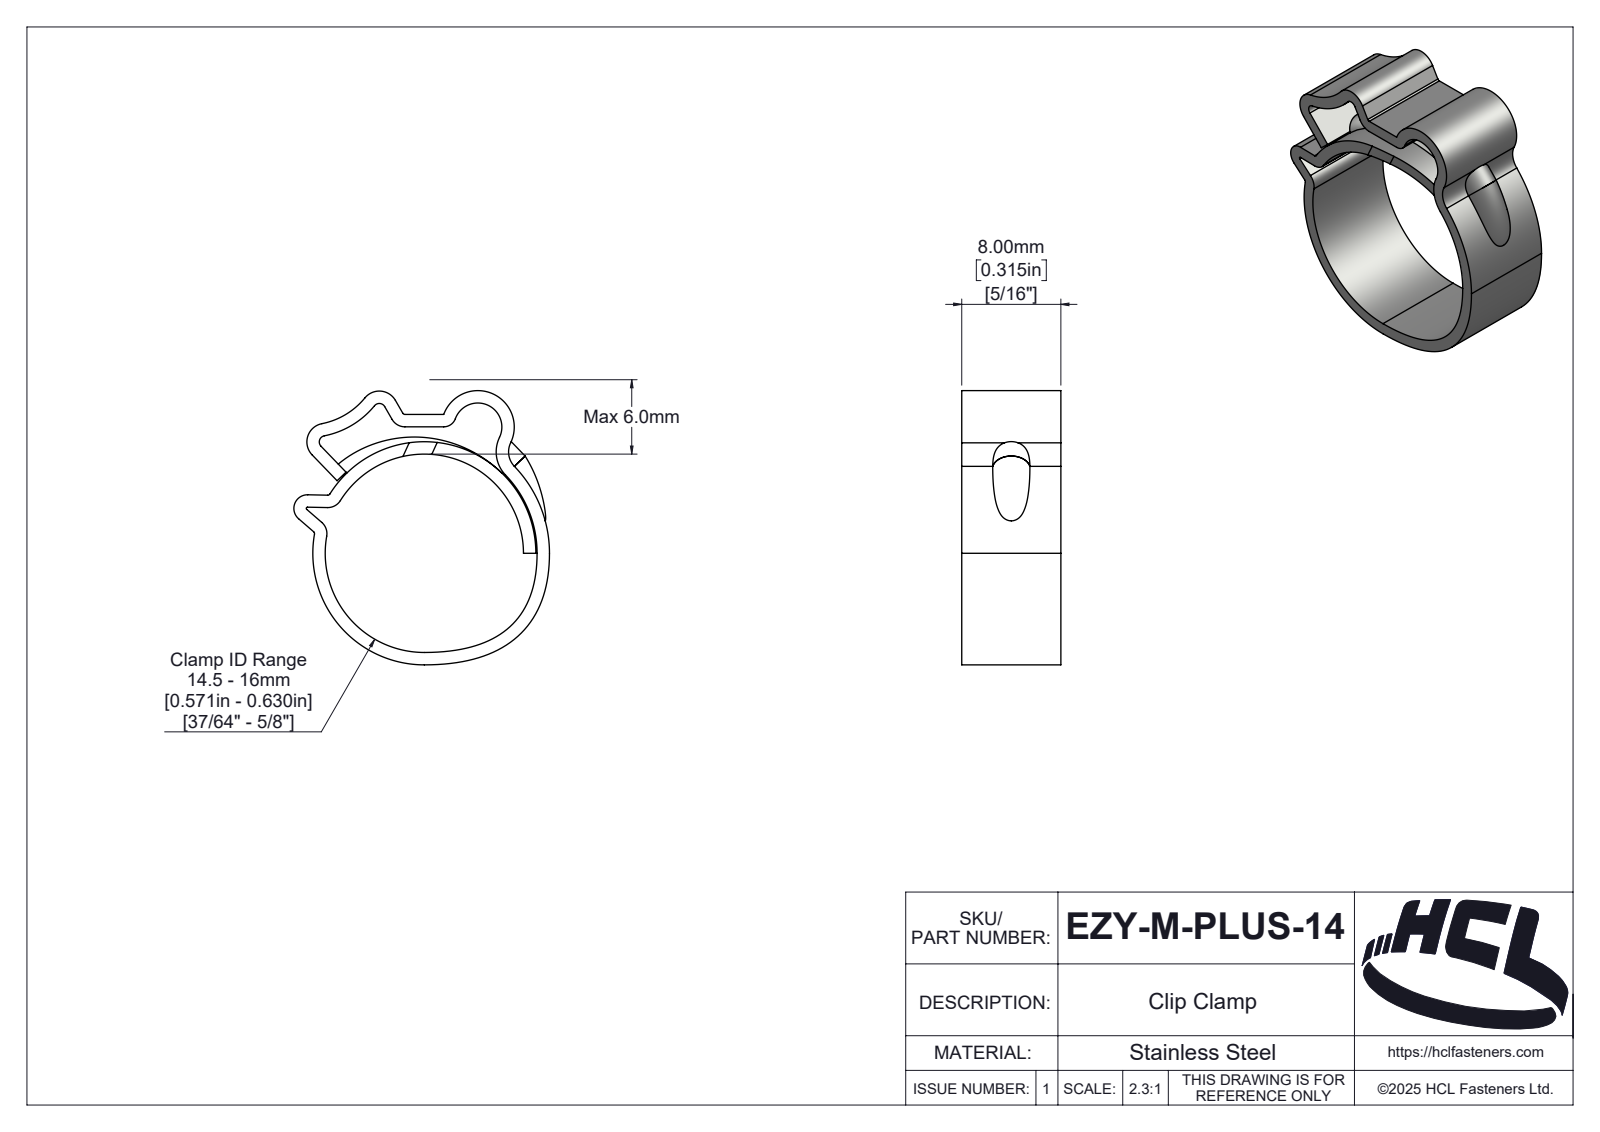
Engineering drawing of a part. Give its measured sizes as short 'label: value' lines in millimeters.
name: EZY-M-PLUS-14
written by: SolidWorks 2025 (AUTOMOTIVE_DESIGN)
unit: mm
bodies: 2 solids, 171 faces (21 planar, 86 cylindrical, 64 other)
size: 22.12 × 20.63 × 8
volume: 724 mm³; area: 1 648 mm²
rounds: 3× R0.2, 3× R1.2, 2× R0.5, 2× R1.5, 2× R10, 1× R0.1, 1× R0.23, 1× R0.94
face distances: 1, 8, 10.2, 11.2
